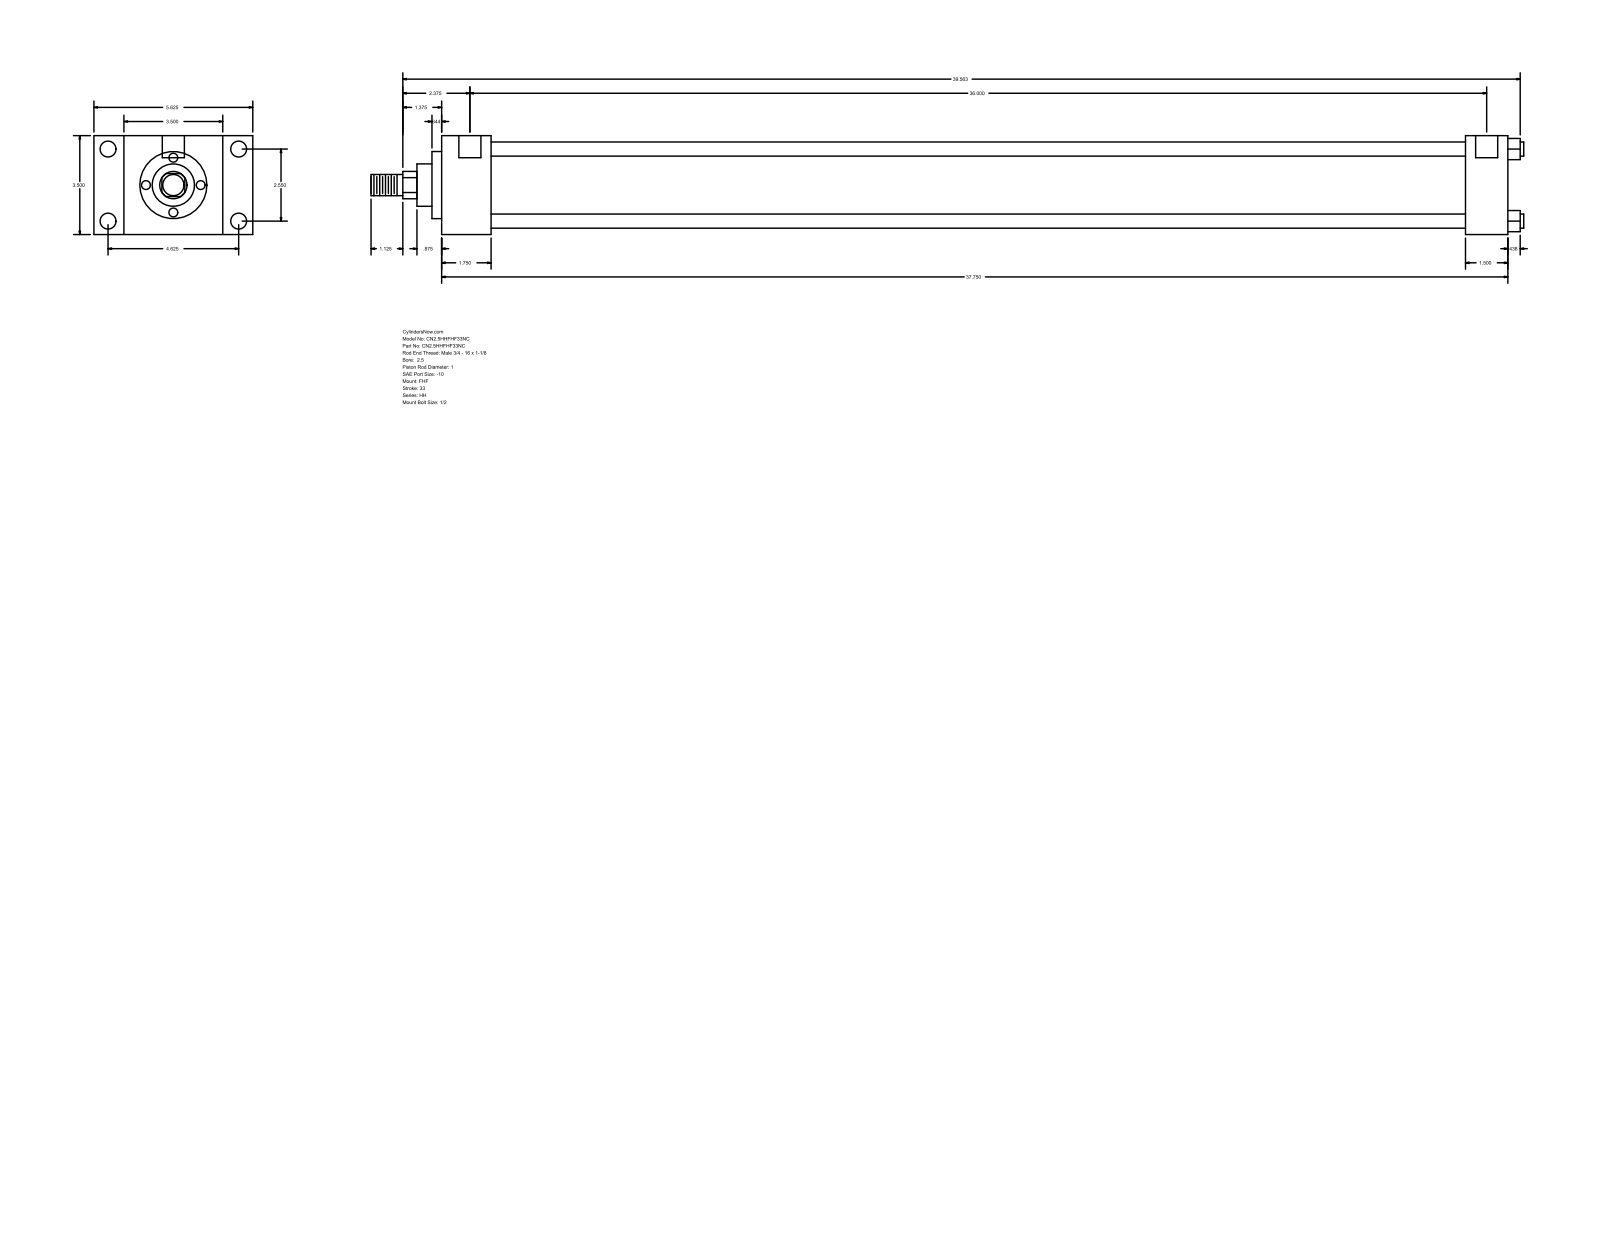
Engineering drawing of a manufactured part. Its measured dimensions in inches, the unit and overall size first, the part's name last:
Units: inches
Overall size (bounding box): 40.813 × 5.625 × 3.5
Round holes (diameter × count): ⌀0.219 ×4, ⌀0.563 ×4, ⌀0.781 ×2
Round bosses / shafts (diameter × count): ⌀0.5 ×4, ⌀2.875 ×1, ⌀2.375 ×1, ⌀1.5 ×1, ⌀1 ×1, ⌀0.75 ×1
Partial cylindrical surfaces — rounded edges, fillets, slot ends (radius × count): R0.484 ×1
Main face-to-face distances: 3.5, 1.75, 1.063, 4.563, 37.75, 36, 5.625, 1.5, 36.25, 34.5
Hole centre spacings: 2.55, 4.625, 5.281, 36.125, 0.062, 0.063, 36, 36.062
Bodies: 0 solids, 90 faces (61 planar, 29 cylindrical, 0 other)
Part name (STEP PRODUCT): HH_FHF__0250_1
STEP written by: GSSL Pune (CONFIG_CONTROL_DESIGN)
